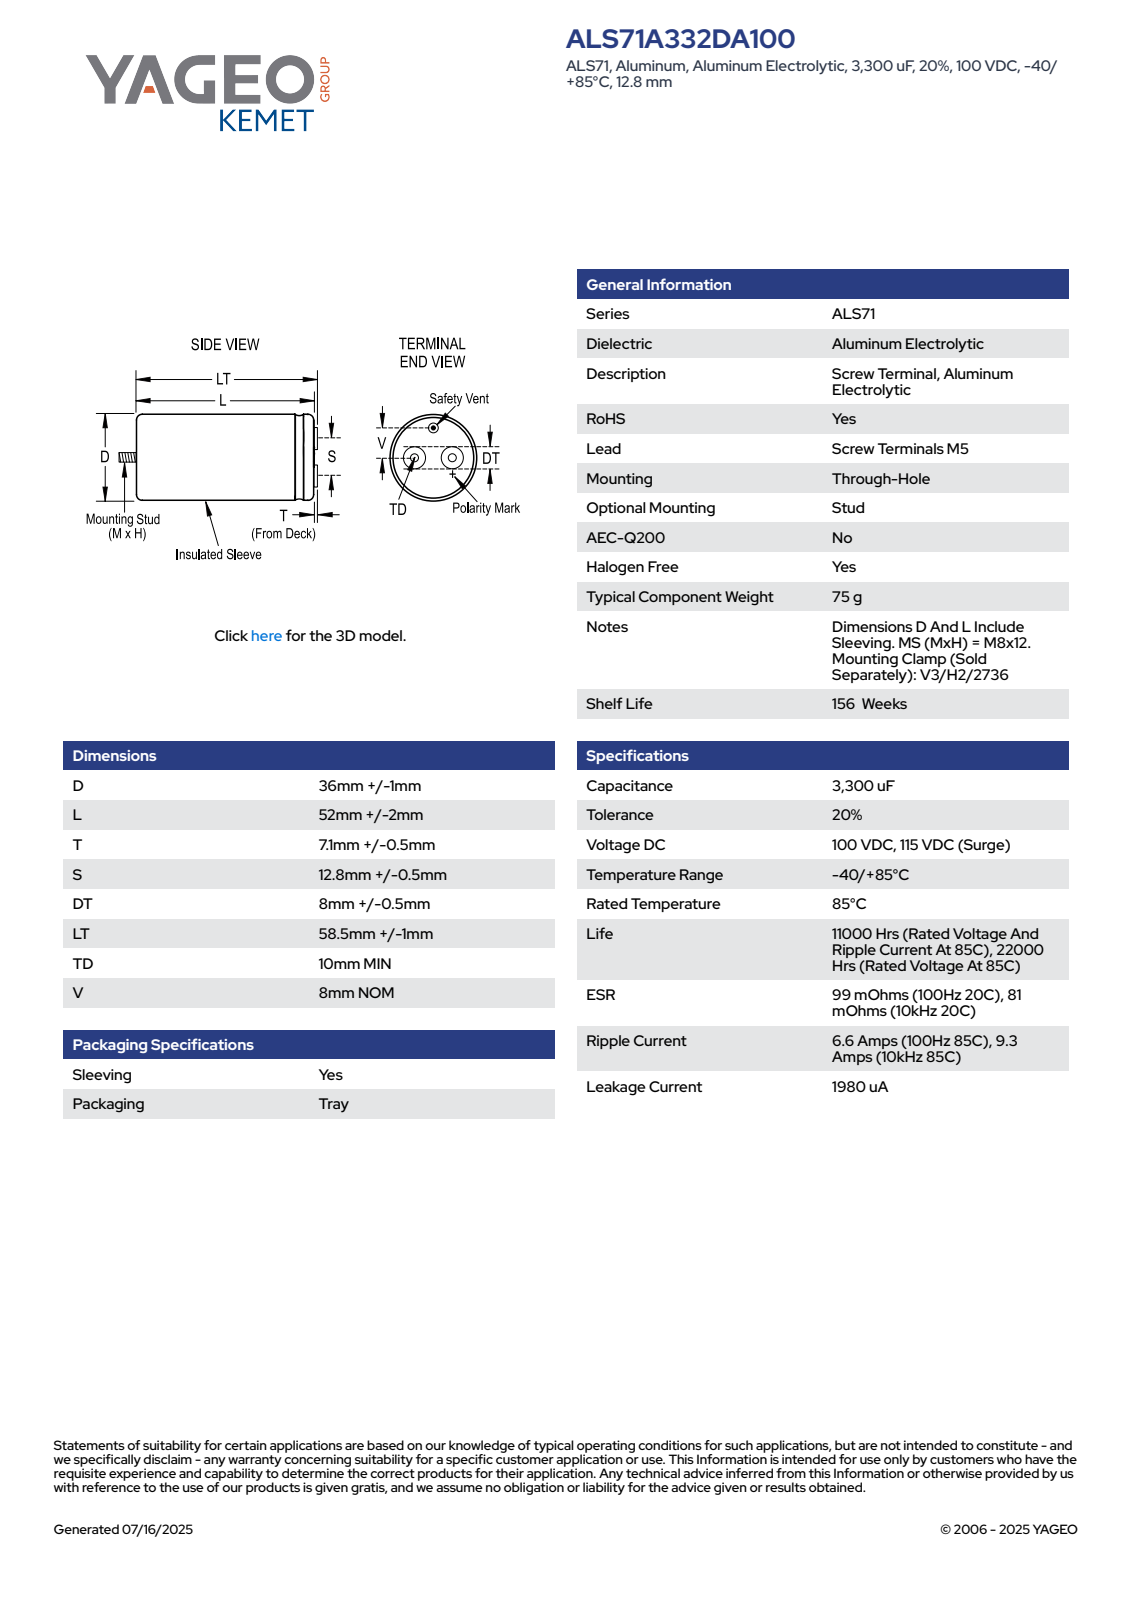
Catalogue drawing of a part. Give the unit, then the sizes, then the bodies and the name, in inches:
Units: inches
Overall size (bounding box): 3.055 × 1.457 × 1.457
Round holes (diameter × count): ⌀0.197 ×2, ⌀0.052 ×1
Round bosses / shafts (diameter × count): ⌀0.335 ×2, ⌀1.457 ×1, ⌀0.472 ×1, ⌀0.089 ×1
Partial cylindrical surfaces — rounded edges, fillets, slot ends (radius × count): R0.729 ×1
Main face-to-face distances: 2.126, 0.63, 2.756, 3.055, 2.425, 0.299, 2.661, 2.031, 0.094, 0.394
Hole centre spacings: 0.403, 0.504
Volume: 3.665 in³ · Surface area: 14.82 in²
Bodies: 1 solid, 97 faces (31 planar, 27 cylindrical, 39 other)
Part name (STEP PRODUCT): CARC_KARS_36X52_D37L54T7.6S12.8DT8.500TD10.000V8.000
STEP written by: SolidWorks 2014 (AUTOMOTIVE_DESIGN)
